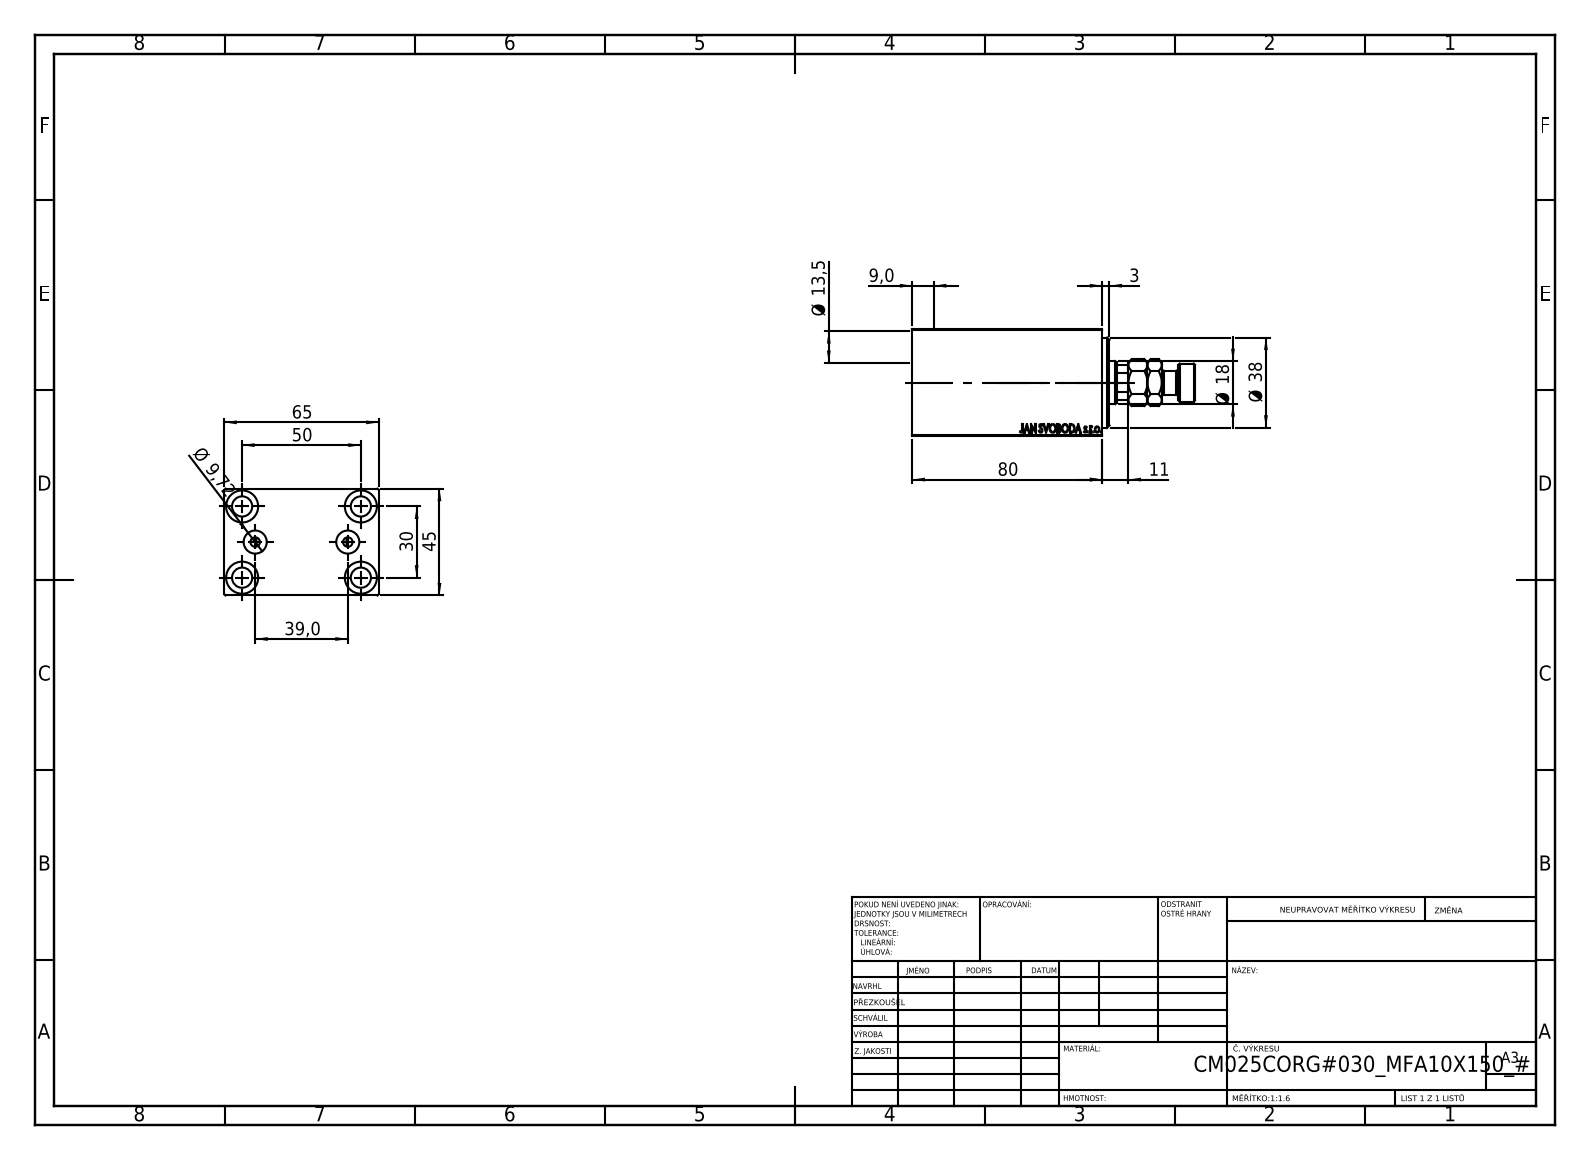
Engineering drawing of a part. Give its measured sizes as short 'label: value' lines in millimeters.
name: MFA; V450CM_C_Body; V450CM_VC_B; V450CM_C_VCP
written by: SolidWorks 2019 (CONFIG_CONTROL_DESIGN)
unit: mm
bodies: 4 solids, 910 faces (424 planar, 60 cylindrical, 426 other)
size: 119 × 65 × 45
volume: 208 777 mm³; area: 53 842 mm²
holes: 5× ⌀8.5, 4× ⌀13.5, 2× ⌀4, 2× ⌀9.72, 1× ⌀18, 1× ⌀21.5, 1× ⌀25, 1× ⌀27, 1× ⌀38
bosses: 1× ⌀16, 1× ⌀10
rounds: 1× R8.5
face distances: 45, 65, 6, 69, 74, 80, 75, 5, 3, 8
hole spacings: 15.98, 29.15, 46.96, 19.5, 30, 50, 58.31, 39
